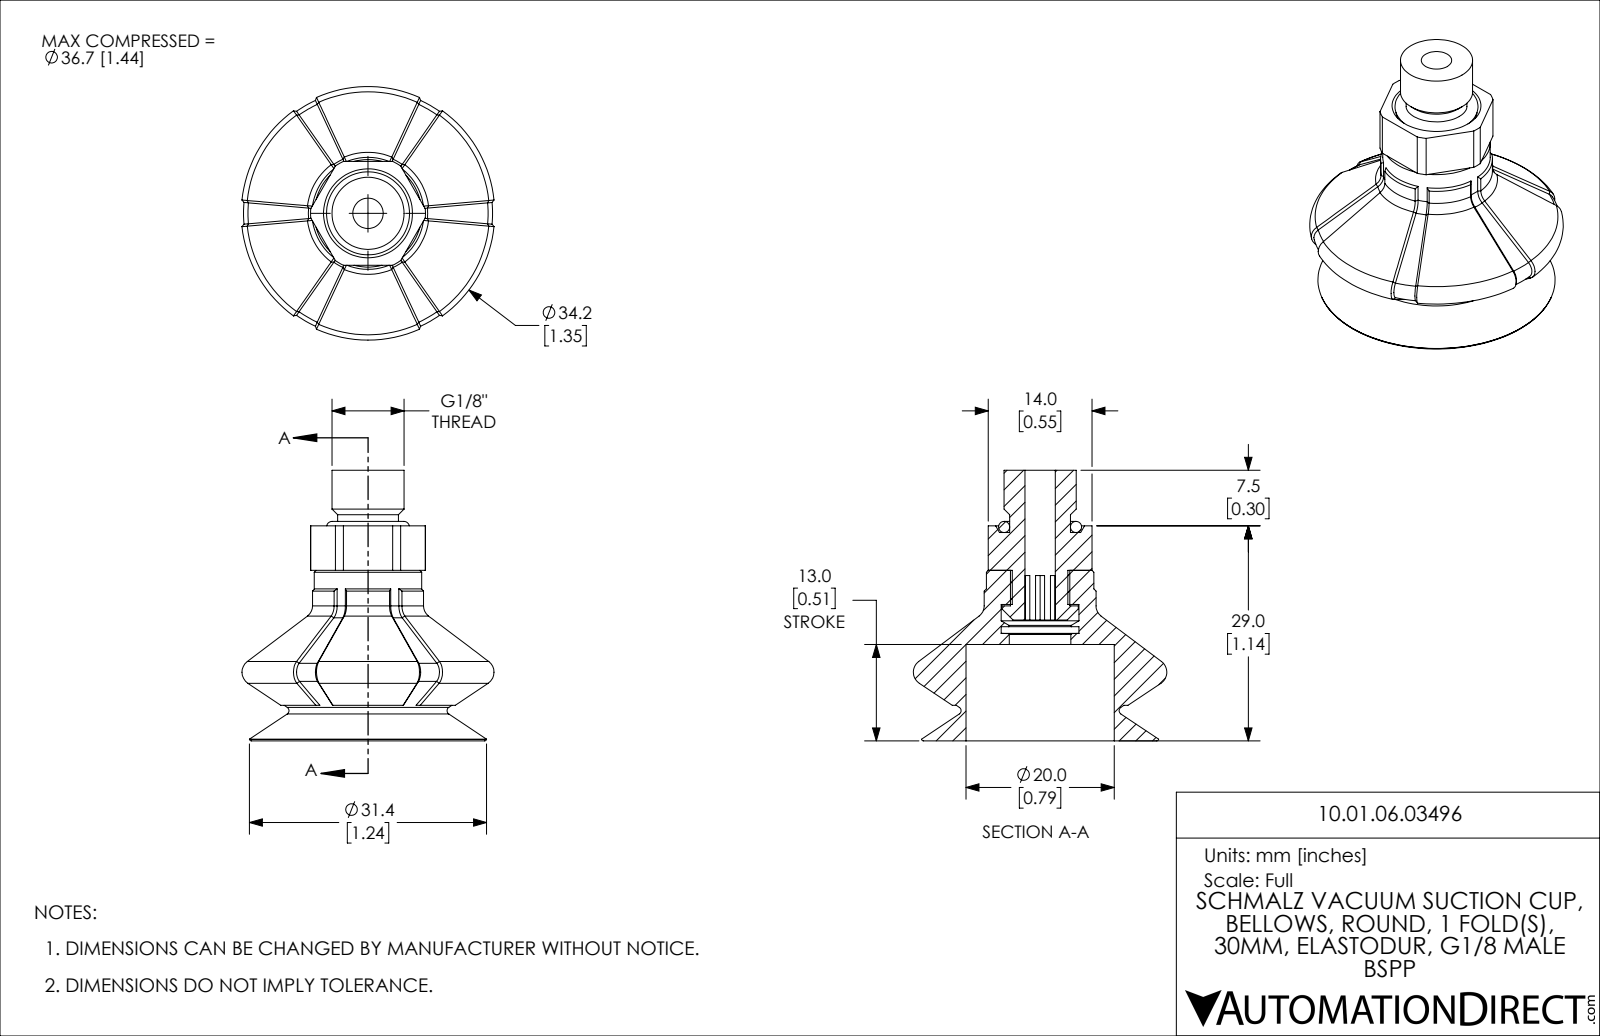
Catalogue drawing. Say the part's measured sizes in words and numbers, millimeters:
The part is named "10.01.06.03496". Its 3-D file was written by "SolidWorks 2021 (CONFIG_CONTROL_DESIGN)". It is 3 solids with 230 faces: 53 planar, 35 cylindrical and 142 other. Overall it measures 36.5 by 34.2 by 34.01 millimeters. Its volume is 7 999 cubic millimeters and its surface area 6 212 square millimeters. Round holes: 1 of diameter 4.1, 1 of diameter 7.5, 1 of diameter 8.3, 1 of diameter 10.5, 1 of diameter 20. Round bosses or shafts: 1 of diameter 14.5, 1 of diameter 10.3, 1 of diameter 9.73, 1 of diameter 8.2, 1 of diameter 8. Partial cylindrical surfaces (rounded edges, fillets, slot ends): 1 of radius 7.55, 1 of radius 7.75. The main face-to-face distances are 13, 23, 10, 14, 10.6, 0.9, 4.8, 18.2, 13.6, 36.5.
